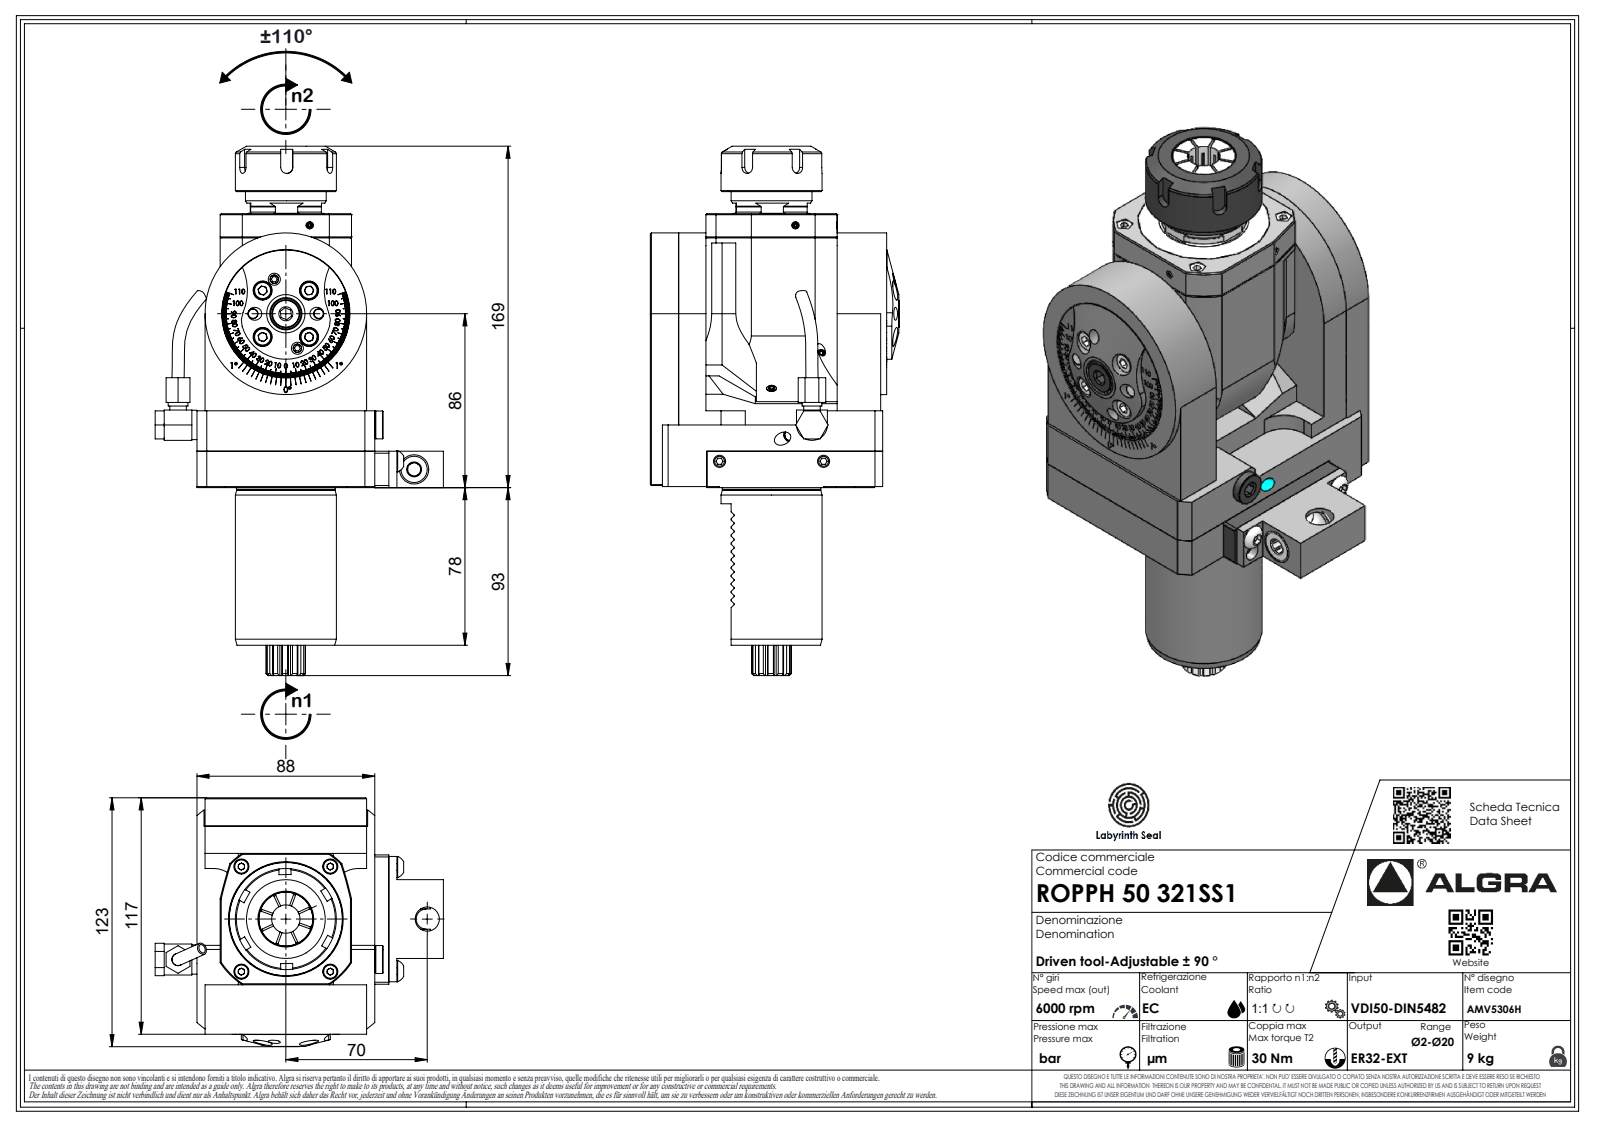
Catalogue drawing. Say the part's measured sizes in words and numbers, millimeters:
The part is named "ROPPH50321SS1". Its 3-D file was written by "SolidWorks 2023 (AUTOMOTIVE_DESIGN)". It is 1 solid with 672 faces: 385 planar, 142 cylindrical and 145 other. Overall it measures 261.91 by 142.7 by 123 millimeters. Its volume is 1 280 000 cubic millimeters and its surface area 112 037 square millimeters. Round holes: 1 of diameter 2.1. Round bosses or shafts: 1 of diameter 80, 1 of diameter 50, 1 of diameter 48.7, 1 of diameter 40, 1 of diameter 14.5, 1 of diameter 9.8, 1 of diameter 8.2, 1 of diameter 6.37. Partial cylindrical surfaces (rounded edges, fillets, slot ends): 24 of radius 9.38, 12 of radius 0.3, 7 of radius 0.33, 7 of radius 0.52, 7 of radius 3.7, 5 of radius 3, 4 of radius 1, 2 of radius 10. The main face-to-face distances are 4, 65, 84, 0.5, 76.5, 11.5, 22.5, 27.5, 7.5, 72.5.
